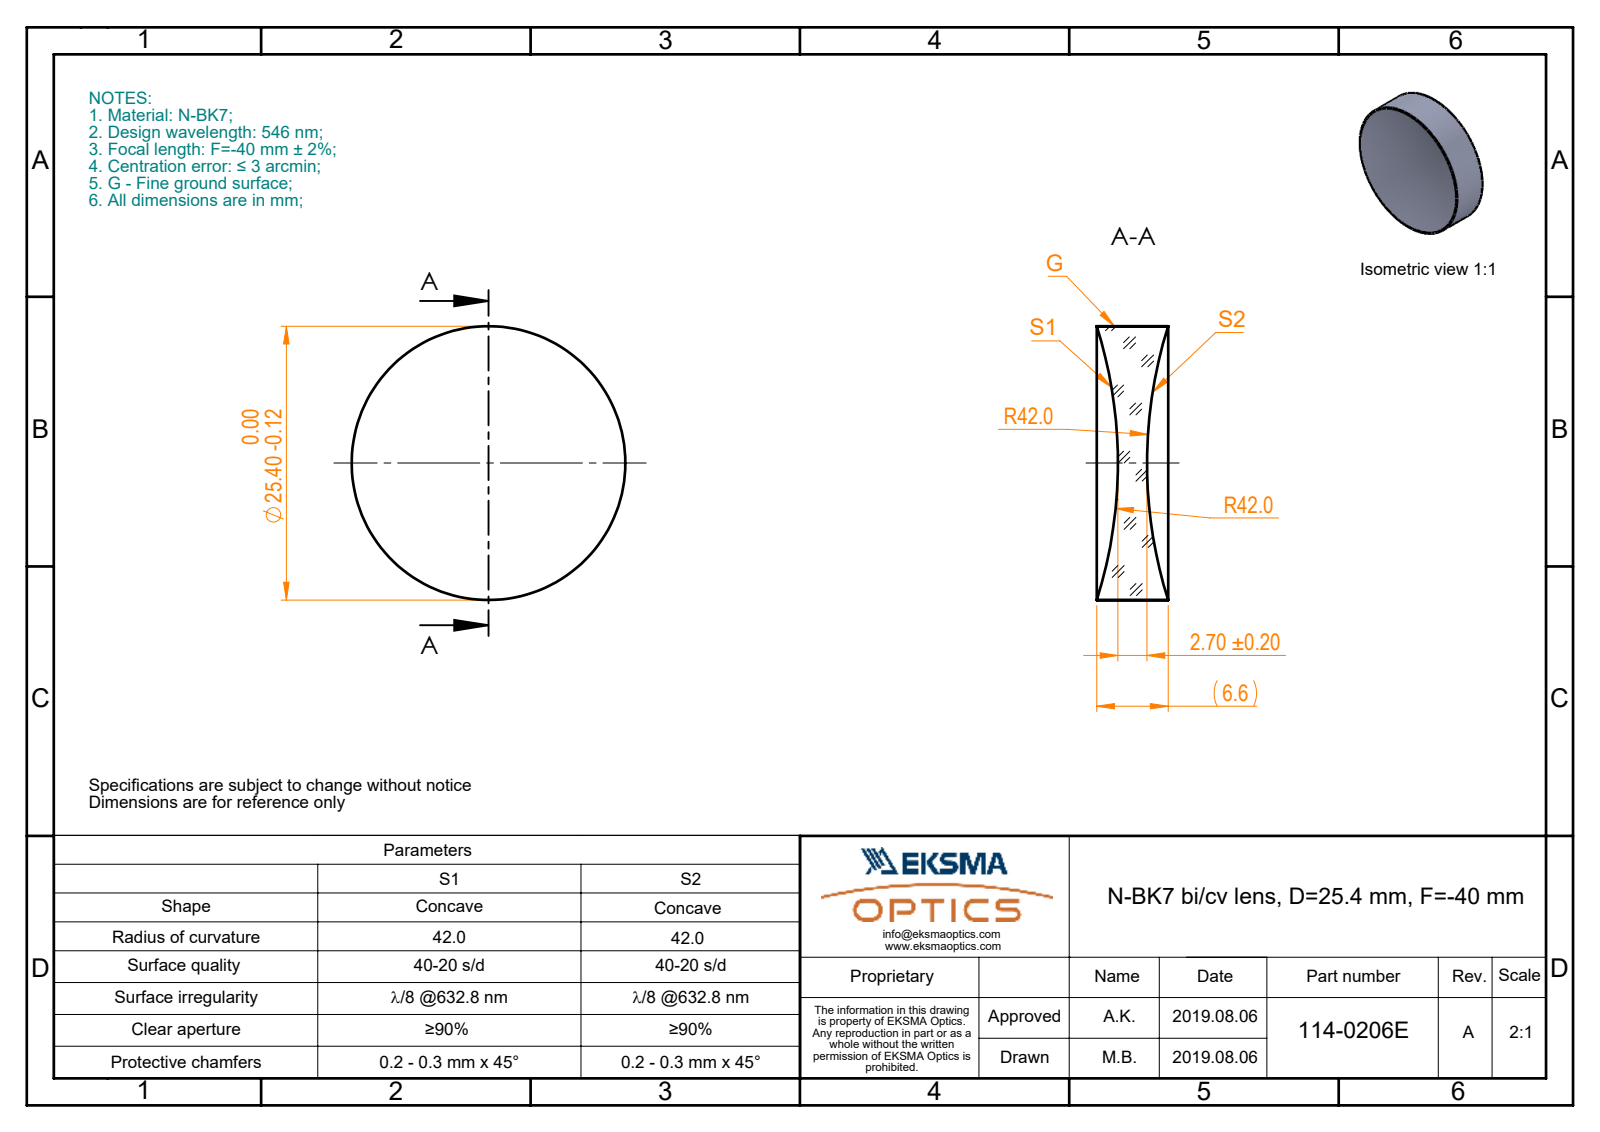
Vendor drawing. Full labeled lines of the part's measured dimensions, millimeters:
Part name (STEP PRODUCT): 114-0206E BK7 bi-cv 25.4 F-40
STEP written by: SolidWorks 2017 (CONFIG_CONTROL_DESIGN)
Units: millimetres
Bodies: 1 solid, 6 faces (0 planar, 2 cylindrical, 4 other)
Overall size (bounding box): 25.4 × 25.4 × 6.64
Volume: 2 358 mm³ · Surface area: 1 567 mm²
Round bosses / shafts (diameter × count): ⌀25.4 ×1
